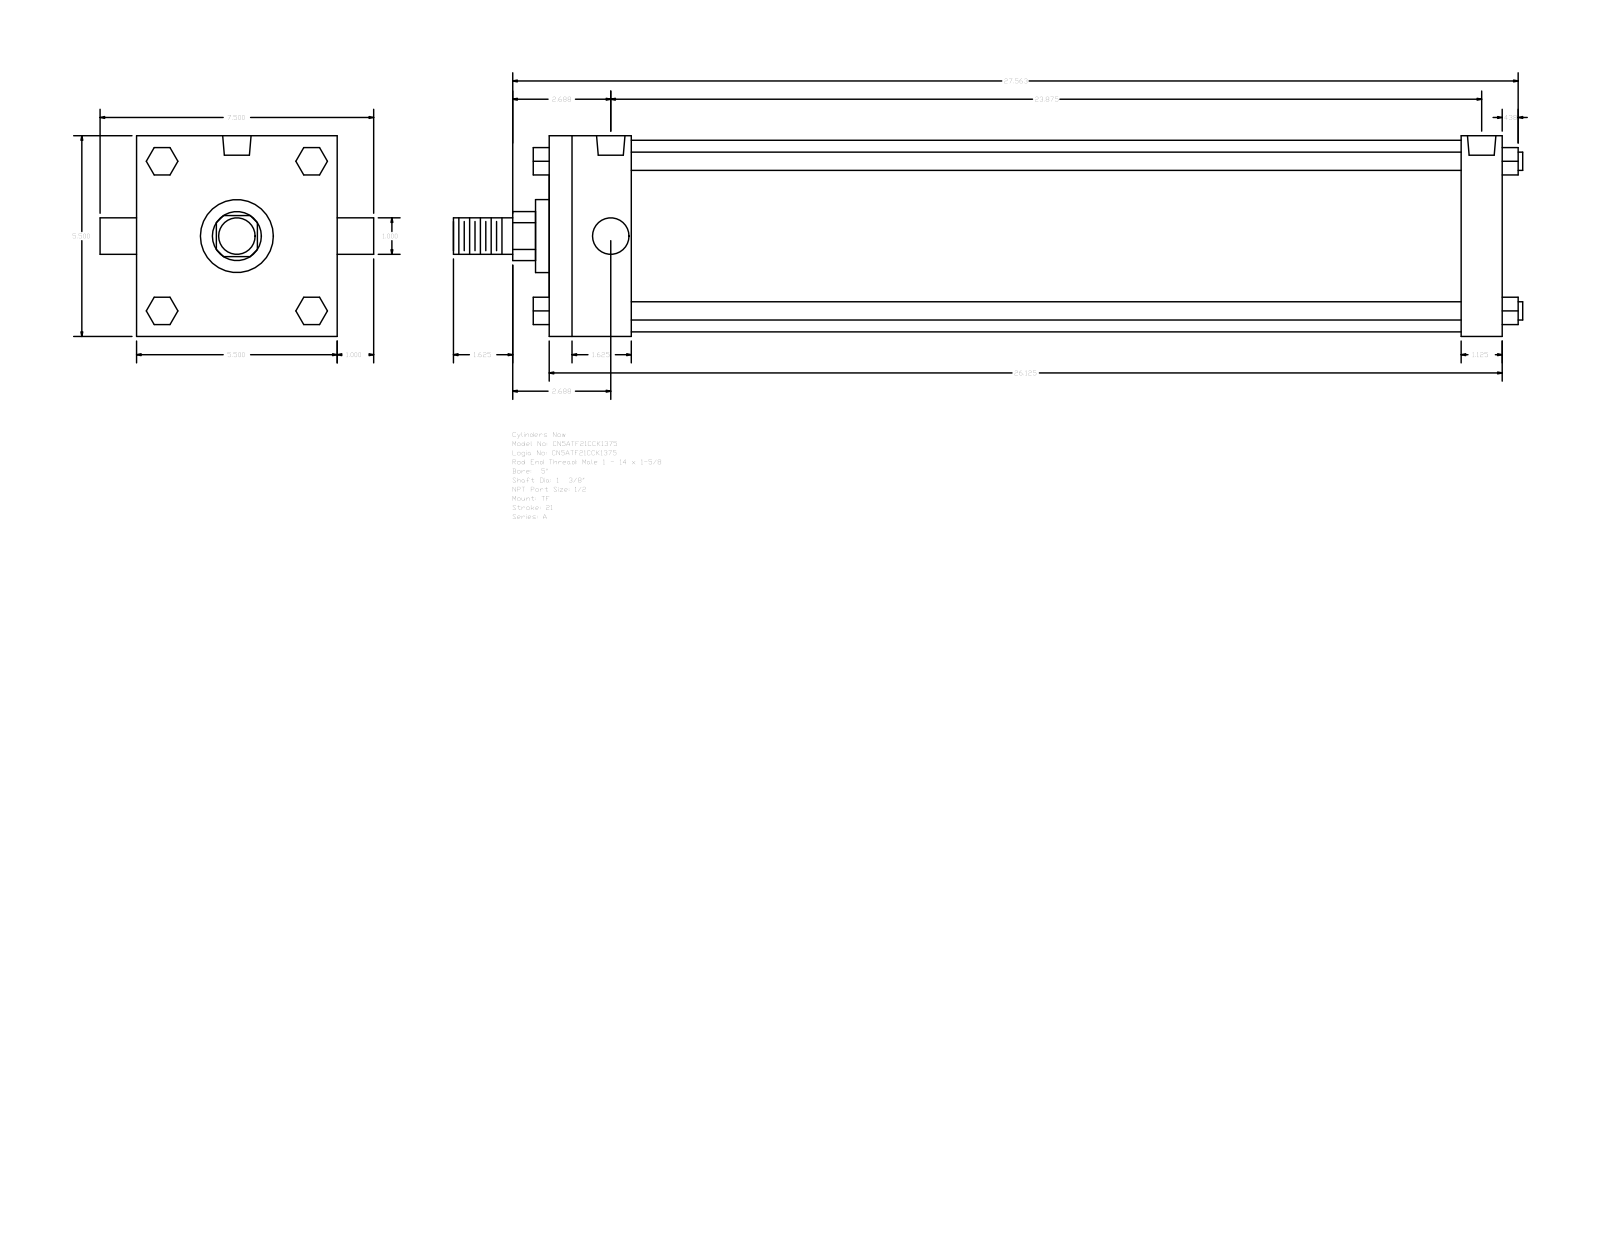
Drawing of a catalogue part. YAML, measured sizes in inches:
part_name: "A_TF__0500_1.375"
step_written_by: "GSSL Pune (CONFIG_CONTROL_DESIGN)"
units: inches
bodies: {solids: 0, faces: 120, planar: 92, cylindrical: 28, other: 0}
overall_size: [29.313, 7.5, 5.5]
round_holes:
  - {diameter: 0.344, count: 3}
  - {diameter: 0.778, count: 2}
round_bosses_or_shafts:
  - {diameter: 0.5, count: 4}
  - {diameter: 1, count: 2}
  - {diameter: 5.25, count: 1}
  - {diameter: 2, count: 1}
  - {diameter: 1.375, count: 1}
partial_cylinders:
  - {radius: 0.672, count: 1}
face_to_face_distances: [5.5, 26.125, 2.25, 1.125, 25, 22.75, 23.875, 0.75, 2.05, 3.55]
hole_center_spacings: [0.094, 23.781, 23.687, 23.875]
